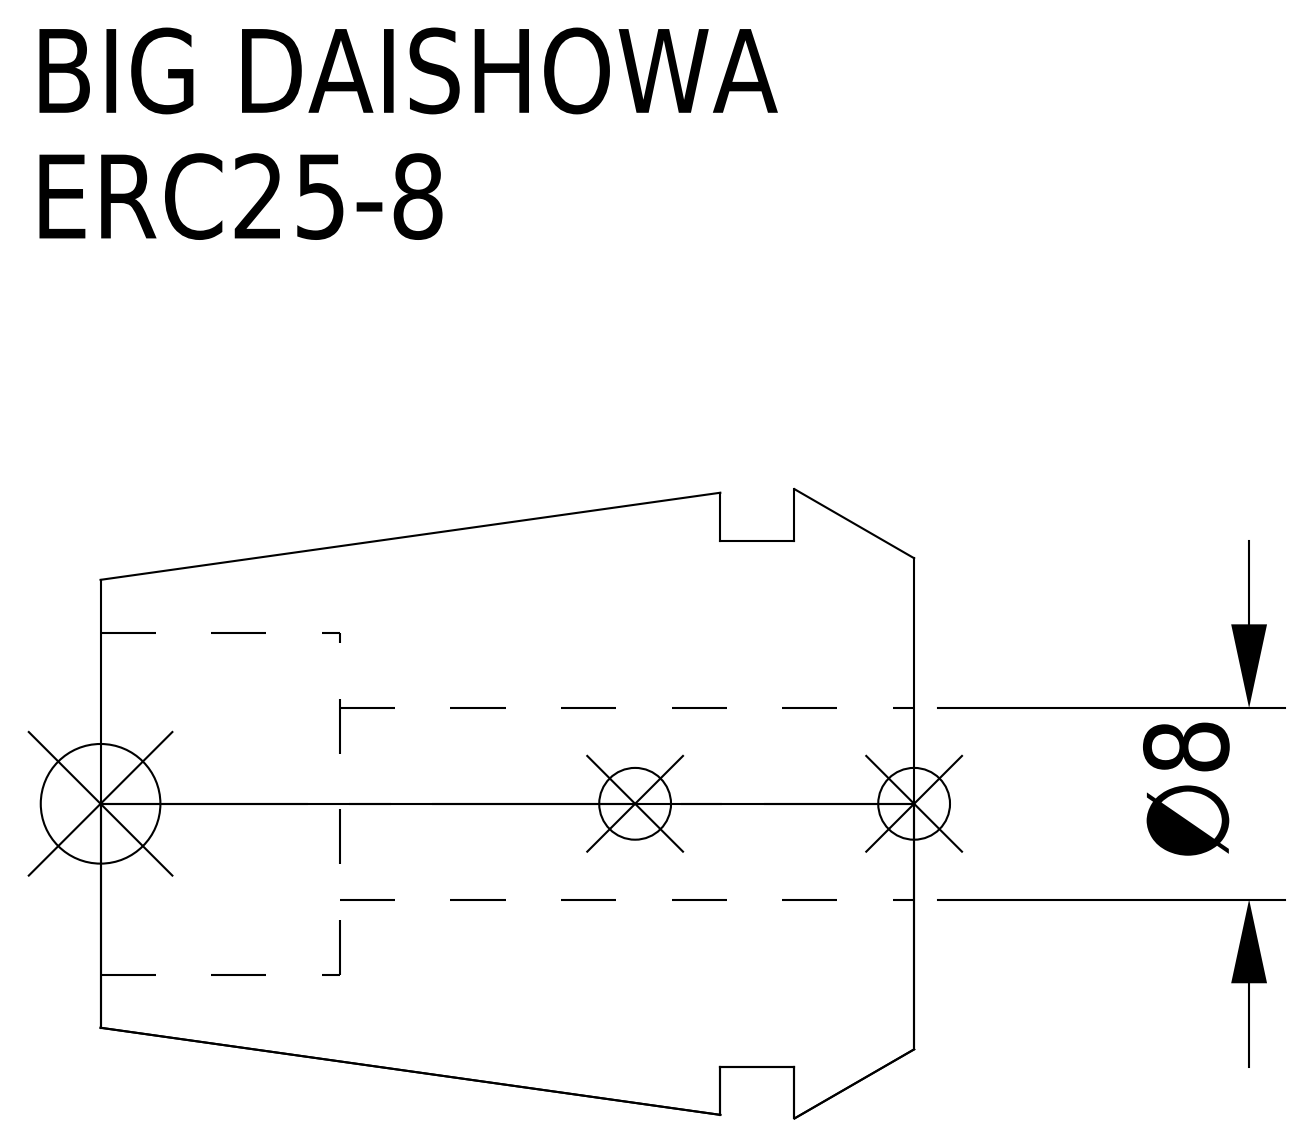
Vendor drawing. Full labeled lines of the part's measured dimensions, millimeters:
Part name (STEP PRODUCT): ERC25-8
STEP written by: CREO PARAMETRIC BY PTC INC, 2016380 (AUTOMOTIVE_DESIGN)
Units: millimetres
Bodies: 1 solid, 15 faces (5 planar, 6 cylindrical, 4 other)
Overall size (bounding box): 34 × 26.3 × 26.3
Volume: 10 790 mm³ · Surface area: 4 348 mm²
Round holes (diameter × count): ⌀8 ×1, ⌀14.3 ×1
Round bosses / shafts (diameter × count): ⌀22 ×1
Main face-to-face distances: 5, 8.1, 3.1, 34, 29, 25.9, 24, 19, 15.9, 10
